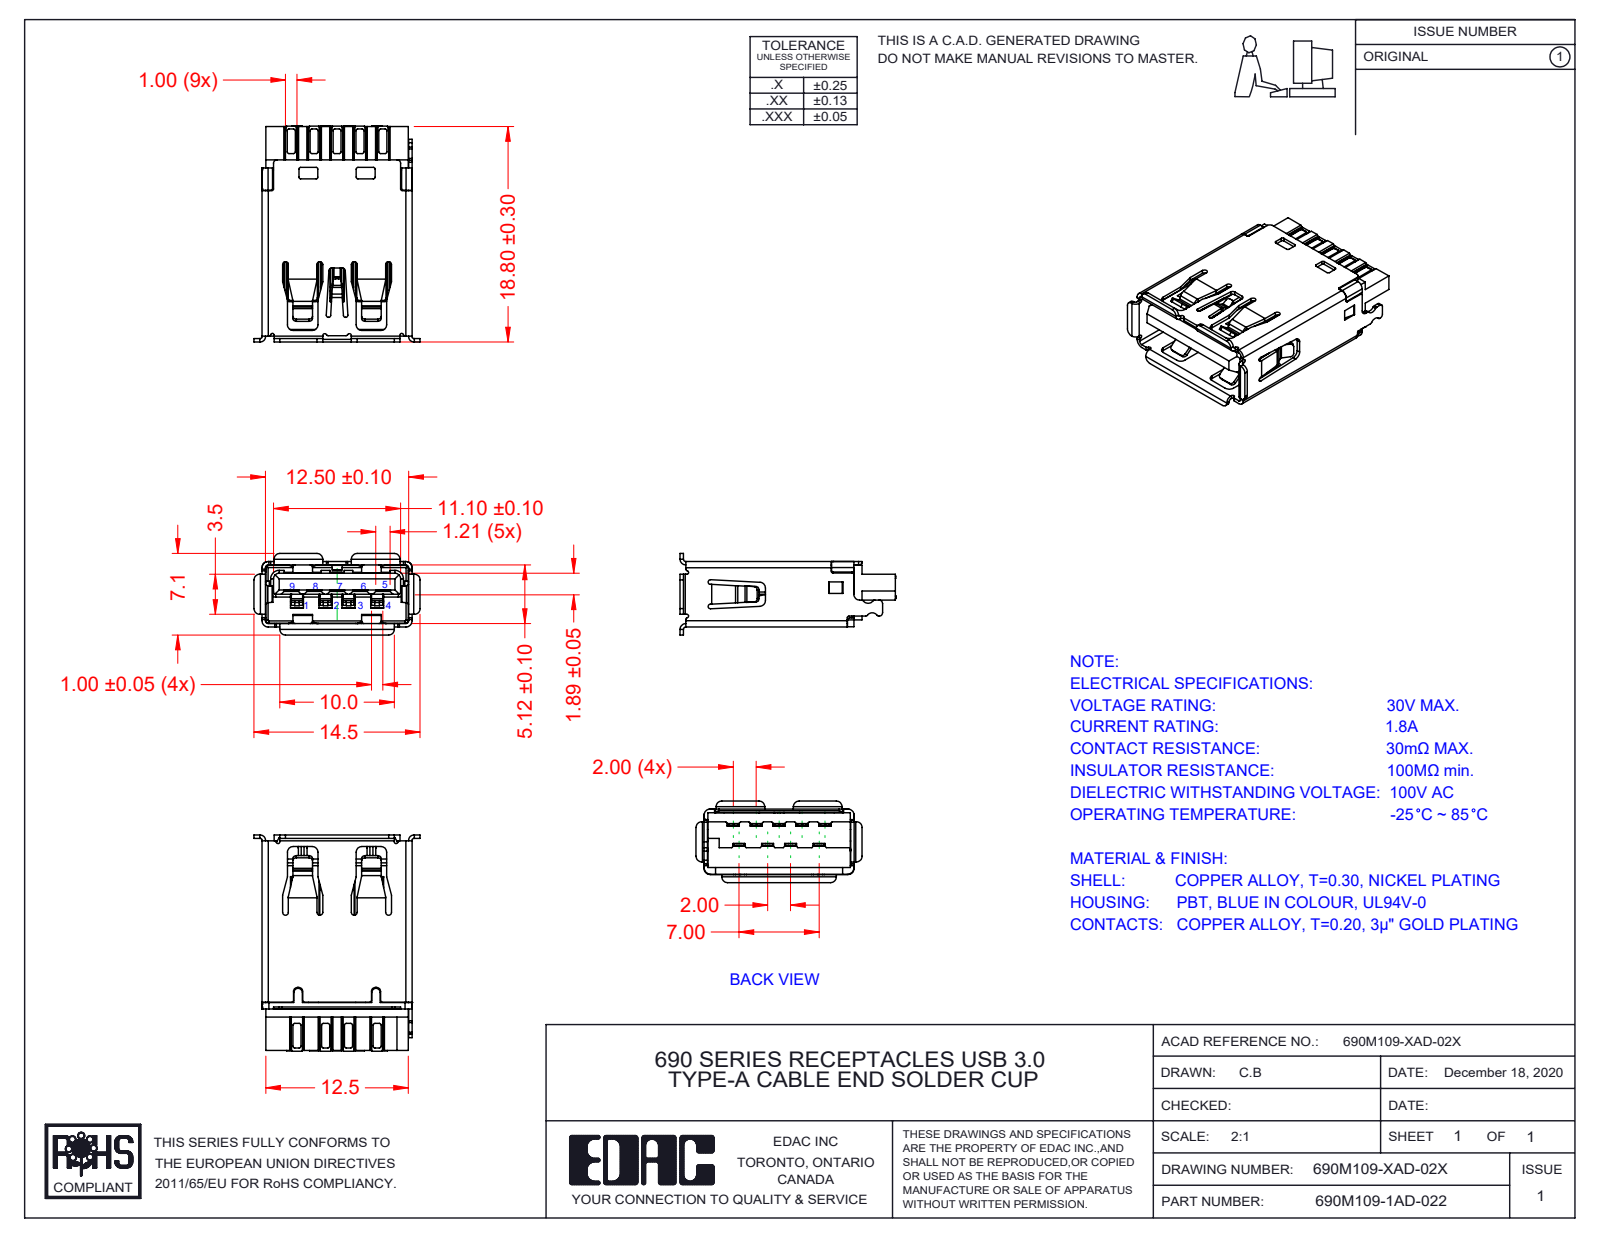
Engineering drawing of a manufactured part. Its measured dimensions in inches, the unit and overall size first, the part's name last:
Units: inches
Overall size (bounding box): 0.743 × 0.571 × 0.28
Partial cylindrical surfaces — rounded edges, fillets, slot ends (radius × count): R0.006 ×128, R0.004 ×46, R0.008 ×36, R0.012 ×32, R0.005 ×30, R0.02 ×26, R0.01 ×20, R0.039 ×13
Main face-to-face distances: 0.213, 0.225, 0.202, 0.013, 0.101, 0.113, 0.046, 0.504, 0.079, 0.014
Volume: 0.039 in³ · Surface area: 4.289 in²
Bodies: 12 solids, 2114 faces (1344 planar, 654 cylindrical, 116 other)
Part name (STEP PRODUCT): Contact5 3.0 690M109-XAD-02X; Shell 690M109-XAD-02X; Contact4 690M109-XAD-02X; 690M109-1AD-022 (+5 more)
STEP written by: SolidWorks 2020 (AUTOMOTIVE_DESIGN)
